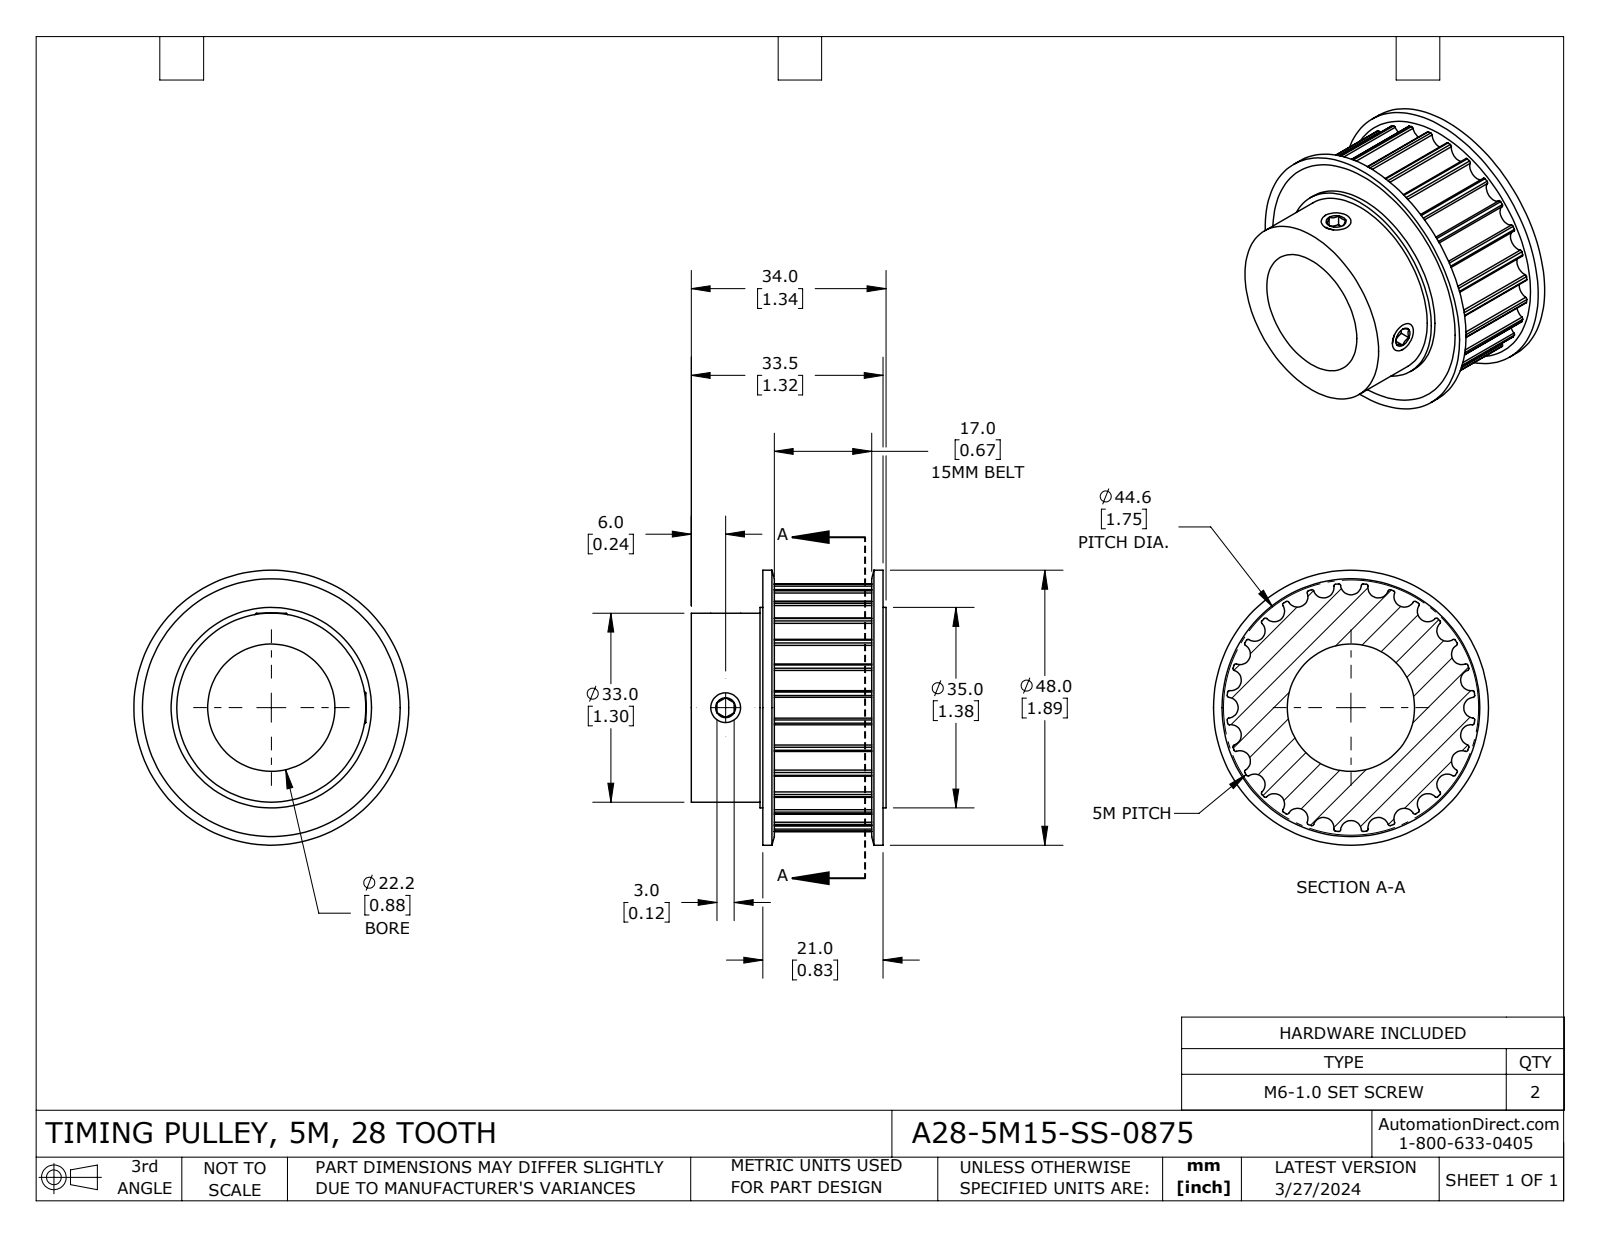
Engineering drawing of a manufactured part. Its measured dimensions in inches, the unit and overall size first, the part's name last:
Units: inches
Overall size (bounding box): 1.89 × 1.89 × 1.339
Round holes (diameter × count): ⌀0.197 ×2, ⌀0.875 ×1, ⌀1.378 ×1
Round bosses / shafts (diameter × count): ⌀0.236 ×2, ⌀1.89 ×1, ⌀1.299 ×1
Partial cylindrical surfaces — rounded edges, fillets, slot ends (radius × count): R0.012 ×56, R0.072 ×28, R0.855 ×1
Main face-to-face distances: 0.063, 0.732, 0.669, 0.035, 0.098, 0.768, 0.831, 0.795, 1.339, 1.303
Volume: 1.647 in³ · Surface area: 21.64 in²
Bodies: 5 solids, 222 faces (25 planar, 163 cylindrical, 34 other)
Part name (STEP PRODUCT): A28-5M15-SS-0875
STEP written by: SolidWorks 2021 (CONFIG_CONTROL_DESIGN)
